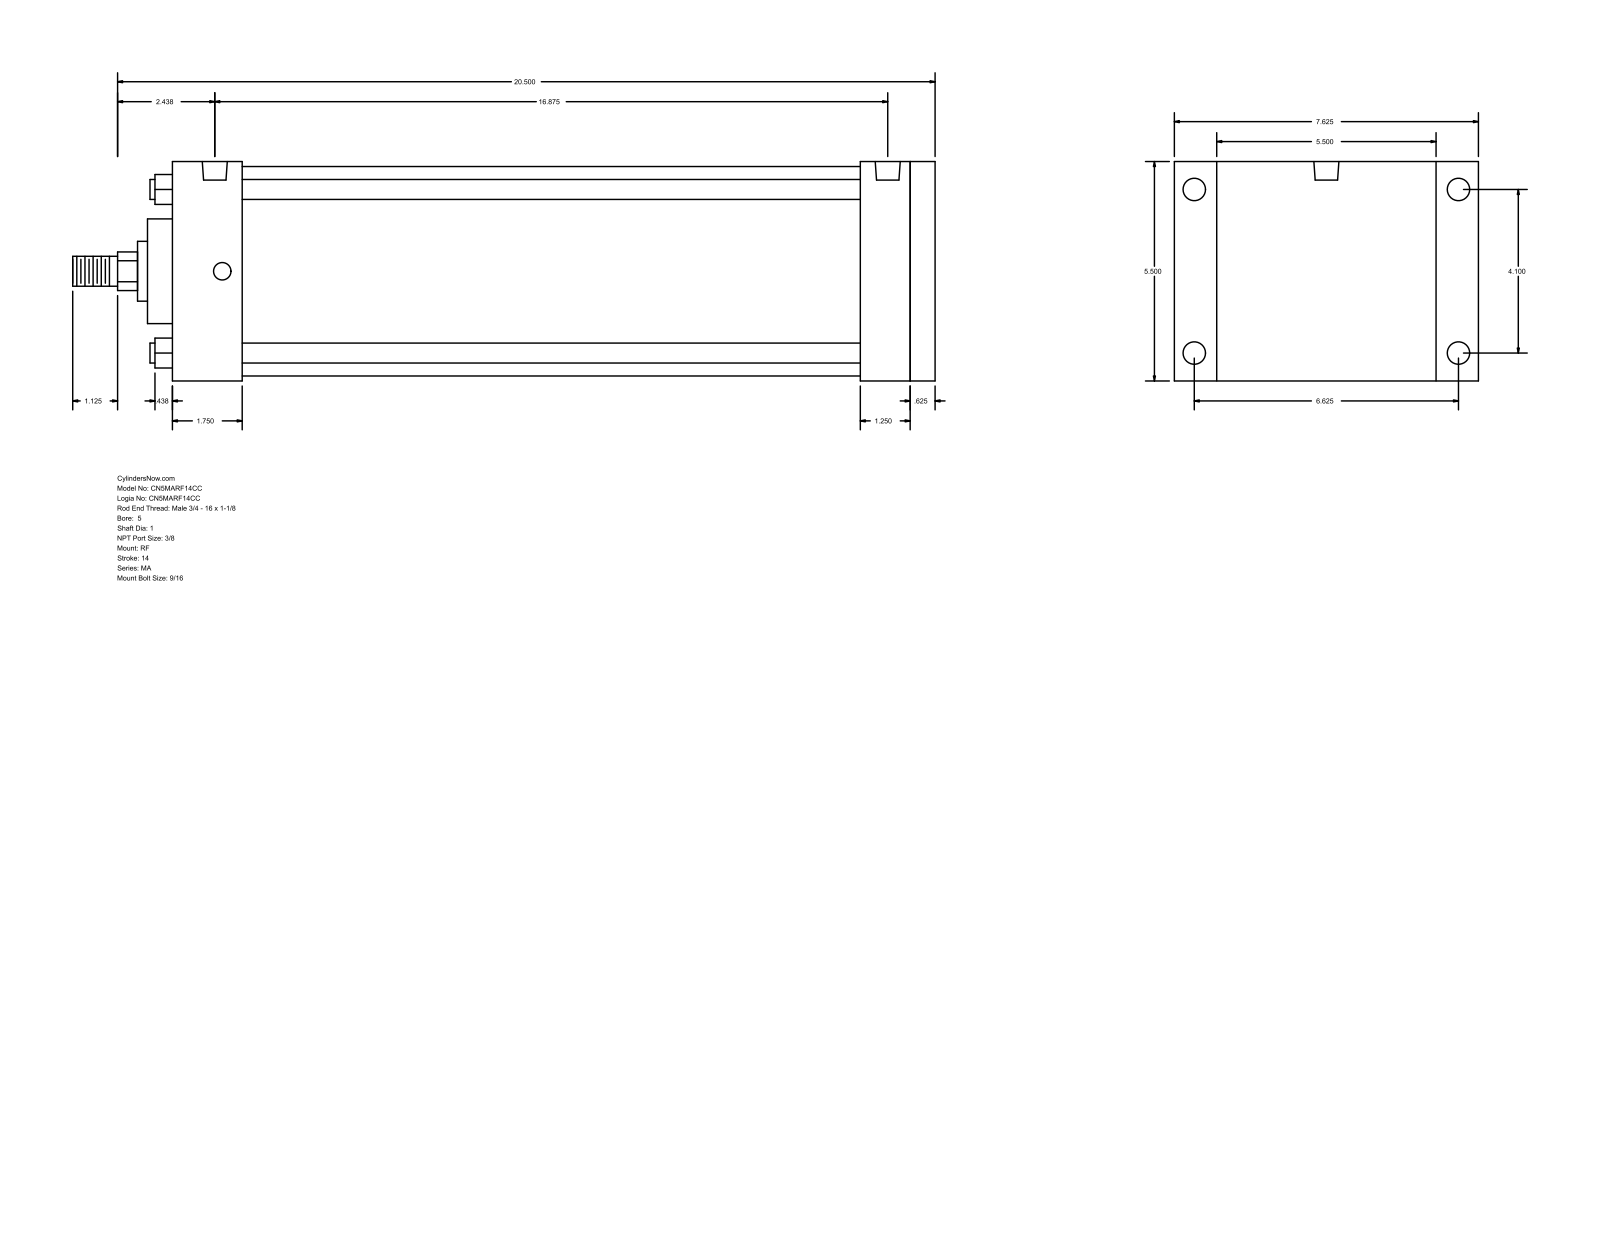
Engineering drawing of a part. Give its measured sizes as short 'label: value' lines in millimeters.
name: MA_RF__0500_1
written by: GSSL Pune (CONFIG_CONTROL_DESIGN)
unit: mm
bodies: 0 solids, 94 faces (65 planar, 29 cylindrical, 0 other)
size: 549.27 × 193.68 × 139.7
holes: 4× ⌀11.11, 4× ⌀14.29, 2× ⌀15.93
bosses: 4× ⌀12.7, 1× ⌀133.35, 1× ⌀66.67, 1× ⌀38.1, 1× ⌀25.4, 1× ⌀19.05
rounds: 1× R12.29
face distances: 139.7, 485.78, 469.9, 15.88, 44.46, 425.44, 441.32, 438.15, 393.69, 31.75
hole spacings: 104.14, 168.28, 197.9, 419.1, 4.76, 4.77, 423.86, 423.87
